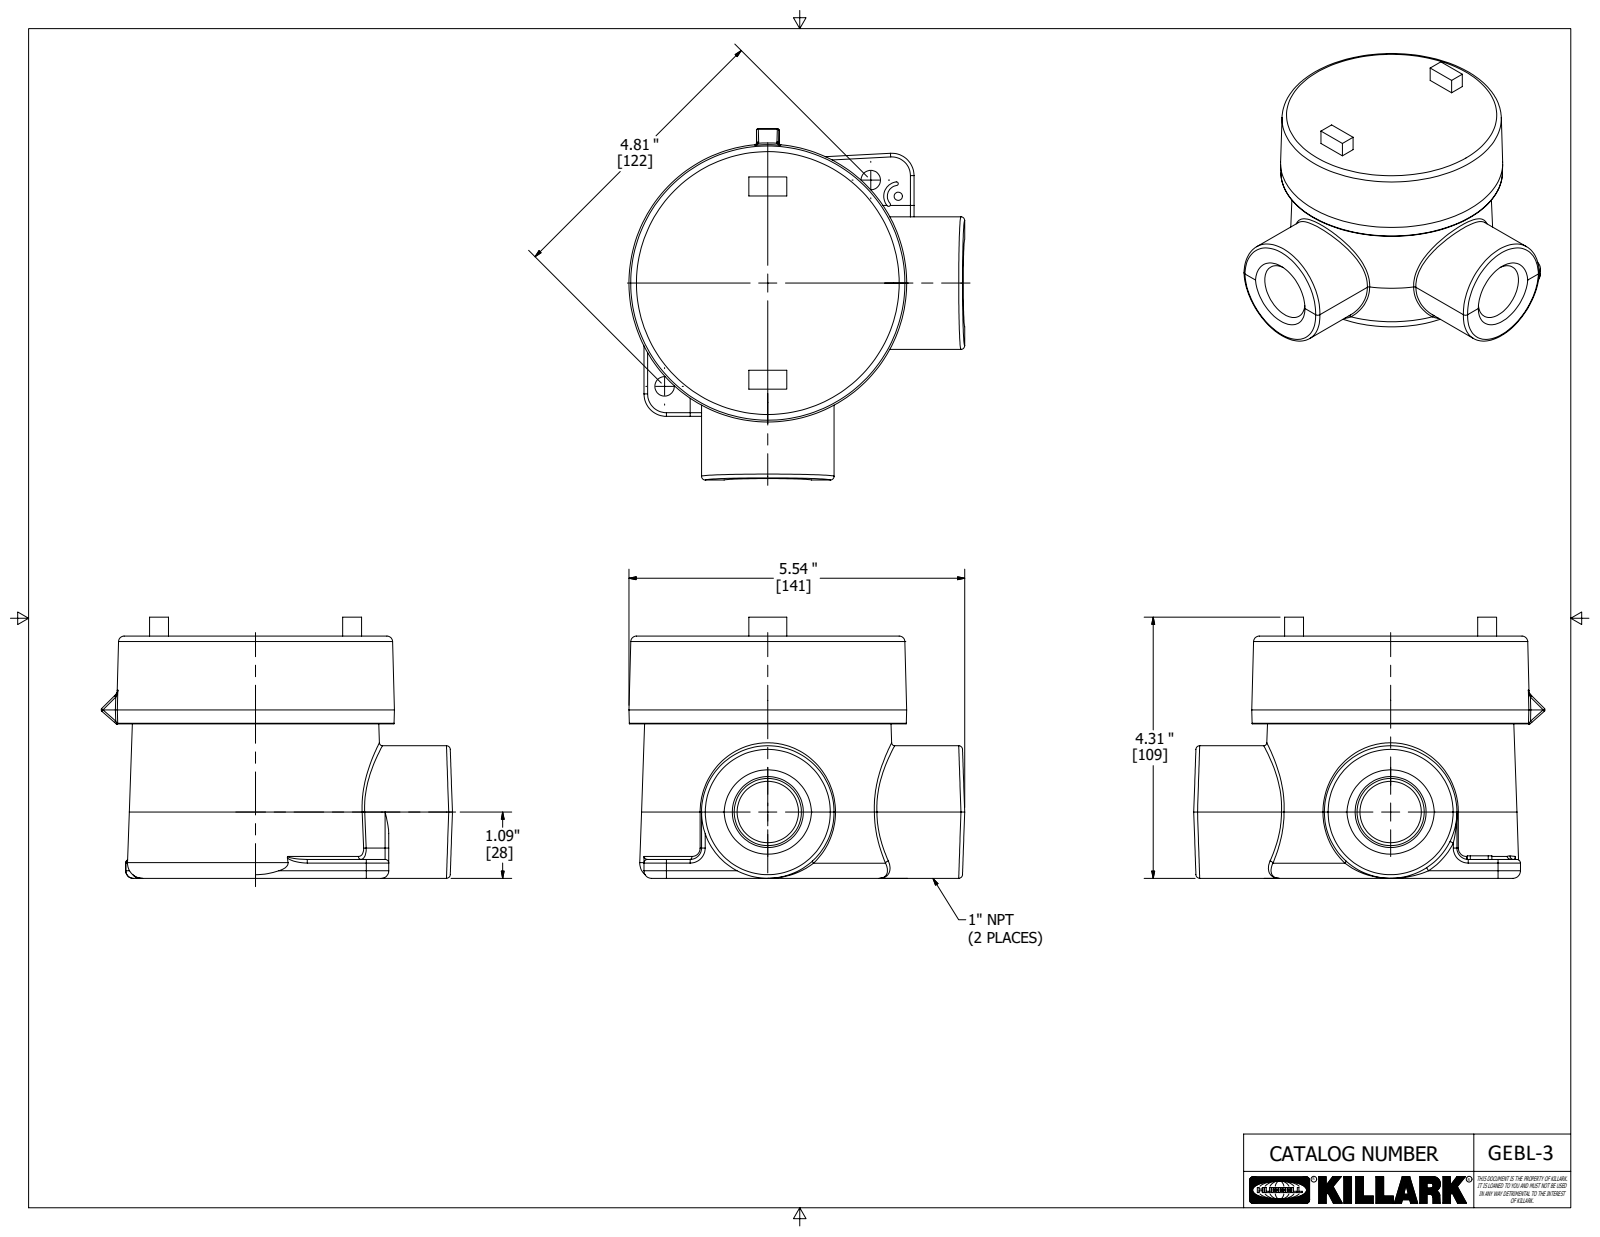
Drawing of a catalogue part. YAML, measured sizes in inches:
part_name: "GEBL-3; 21172; 21147-override"
step_written_by: "Autodesk Inventor 2020 (AUTOMOTIVE_DESIGN)"
units: inches
bodies: {solids: 2, faces: 811, planar: 405, cylindrical: 83, other: 323}
overall_size: [5.798, 5.542, 4.31]
volume: 36.94
surface_area: 200.6
round_holes:
  - {diameter: 0.321, count: 2}
  - {diameter: 1.013, count: 2}
  - {diameter: 1.558, count: 2}
  - {diameter: 0.136, count: 1}
  - {diameter: 3.823, count: 1}
  - {diameter: 4.045, count: 1}
round_bosses_or_shafts:
  - {diameter: 2.188, count: 2}
partial_cylinders:
  - {radius: 0.06, count: 33}
  - {radius: 0.03, count: 12}
  - {radius: 0.125, count: 4}
  - {radius: 0.031, count: 3}
  - {radius: 0.187, count: 2}
  - {radius: 0.37, count: 2}
  - {radius: 0.18, count: 1}
  - {radius: 0.24, count: 1}
face_to_face_distances: [3.998, 3.56, 0.438, 2.549, 1.011, 1.449, 0.38, 2.169, 3.18, 3.618]
hole_center_spacings: [0.527, 2.403, 2.41, 2.586, 4.813, 4.971]
